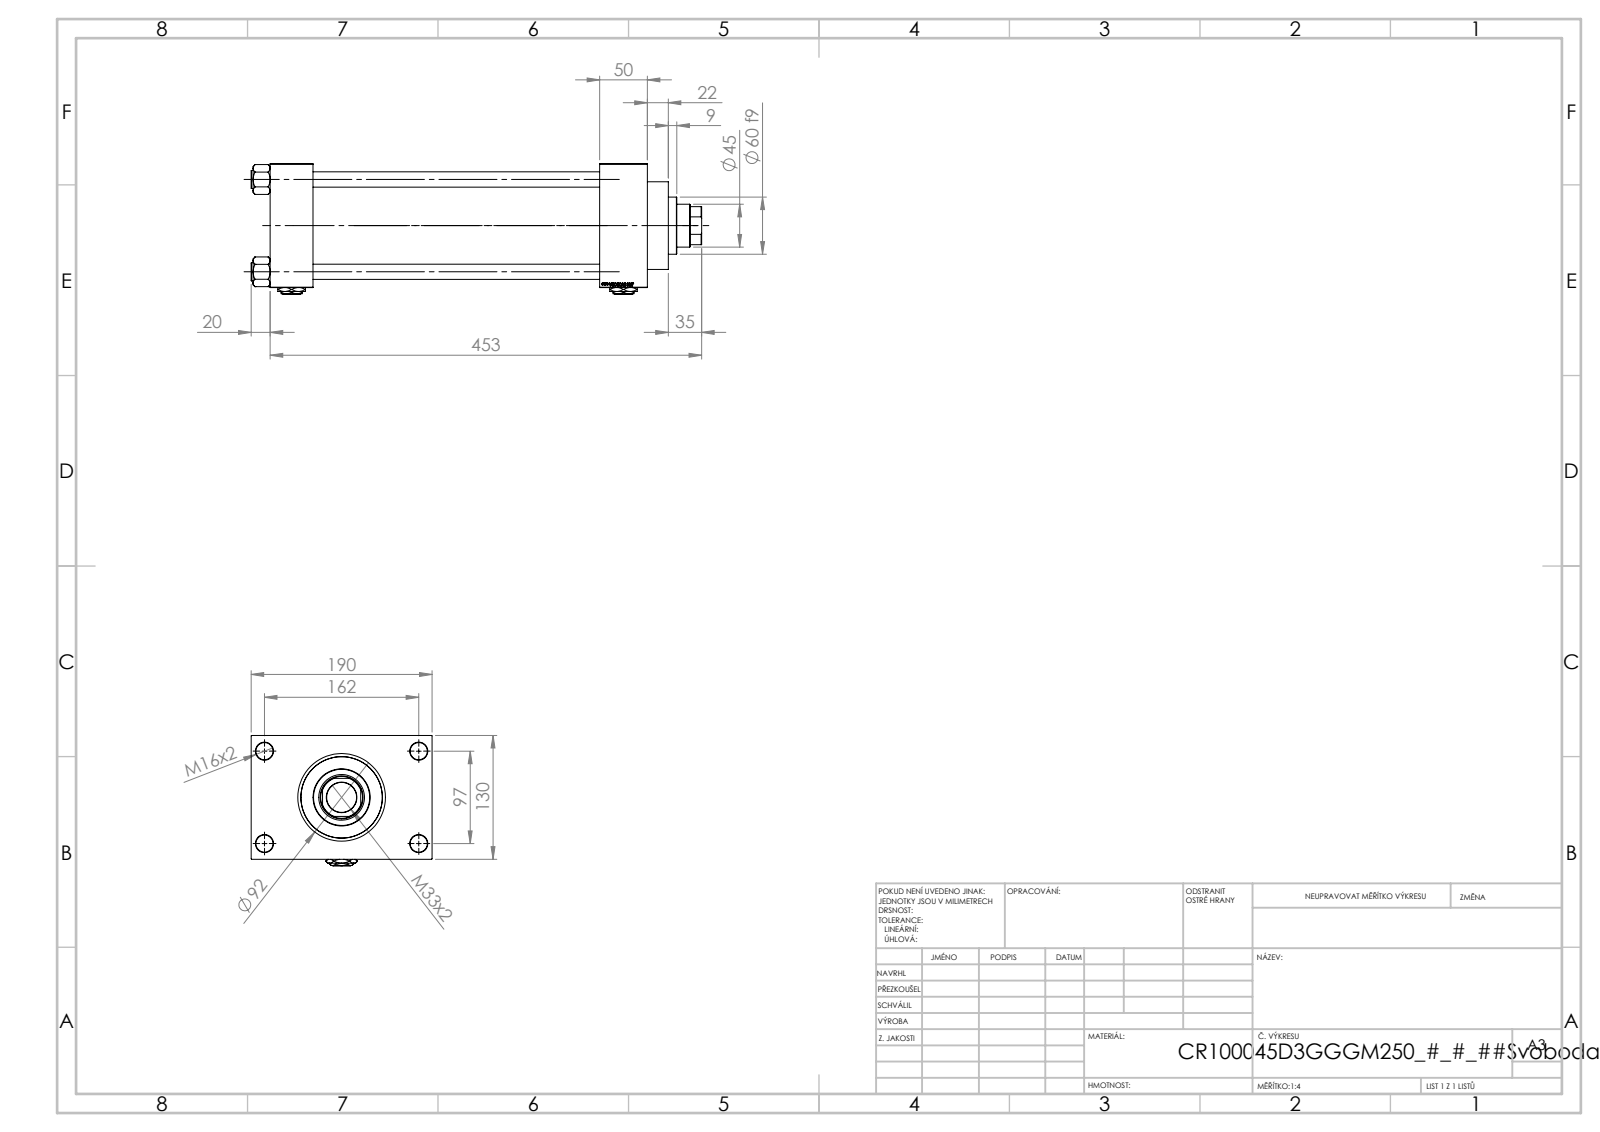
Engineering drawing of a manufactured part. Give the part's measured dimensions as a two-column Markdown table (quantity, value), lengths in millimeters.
| quantity | value |
| --- | --- |
| part name | V215CR_D_Body; NUT_M5_D; V215CR_VCP_D; V215_VC_A (+2 more) |
| STEP written by | SolidWorks 2019 (CONFIG_CONTROL_DESIGN) |
| units | millimeters |
| bodies | 13 solids, 1253 faces (593 planar, 100 cylindrical, 560 other) |
| overall size | 473 × 190 × 137 |
| volume | 3 367 000 mm³ |
| surface area | 586 921 mm² |
| round holes (diameter × count) | 16 × 4, 18 × 4, 7 × 2, 26.44 × 2, 35 × 2, 31.5 × 1, 45 × 1, 48 × 1, 76 × 1, 85.5 × 1, 100 × 1 |
| round bosses / shafts (diameter × count) | 19 × 4, 106 × 1, 92 × 1, 60 × 1 |
| partial cylindrical surfaces (radius × count) | 22 × 1 |
| main face-to-face distances | 130, 45, 346, 301, 396, 351, 50, 30, 160, 190 |
| hole center spacings | 32.55, 68.52, 94.41, 96.9, 102.27, 129.45, 161.73, 97 |
